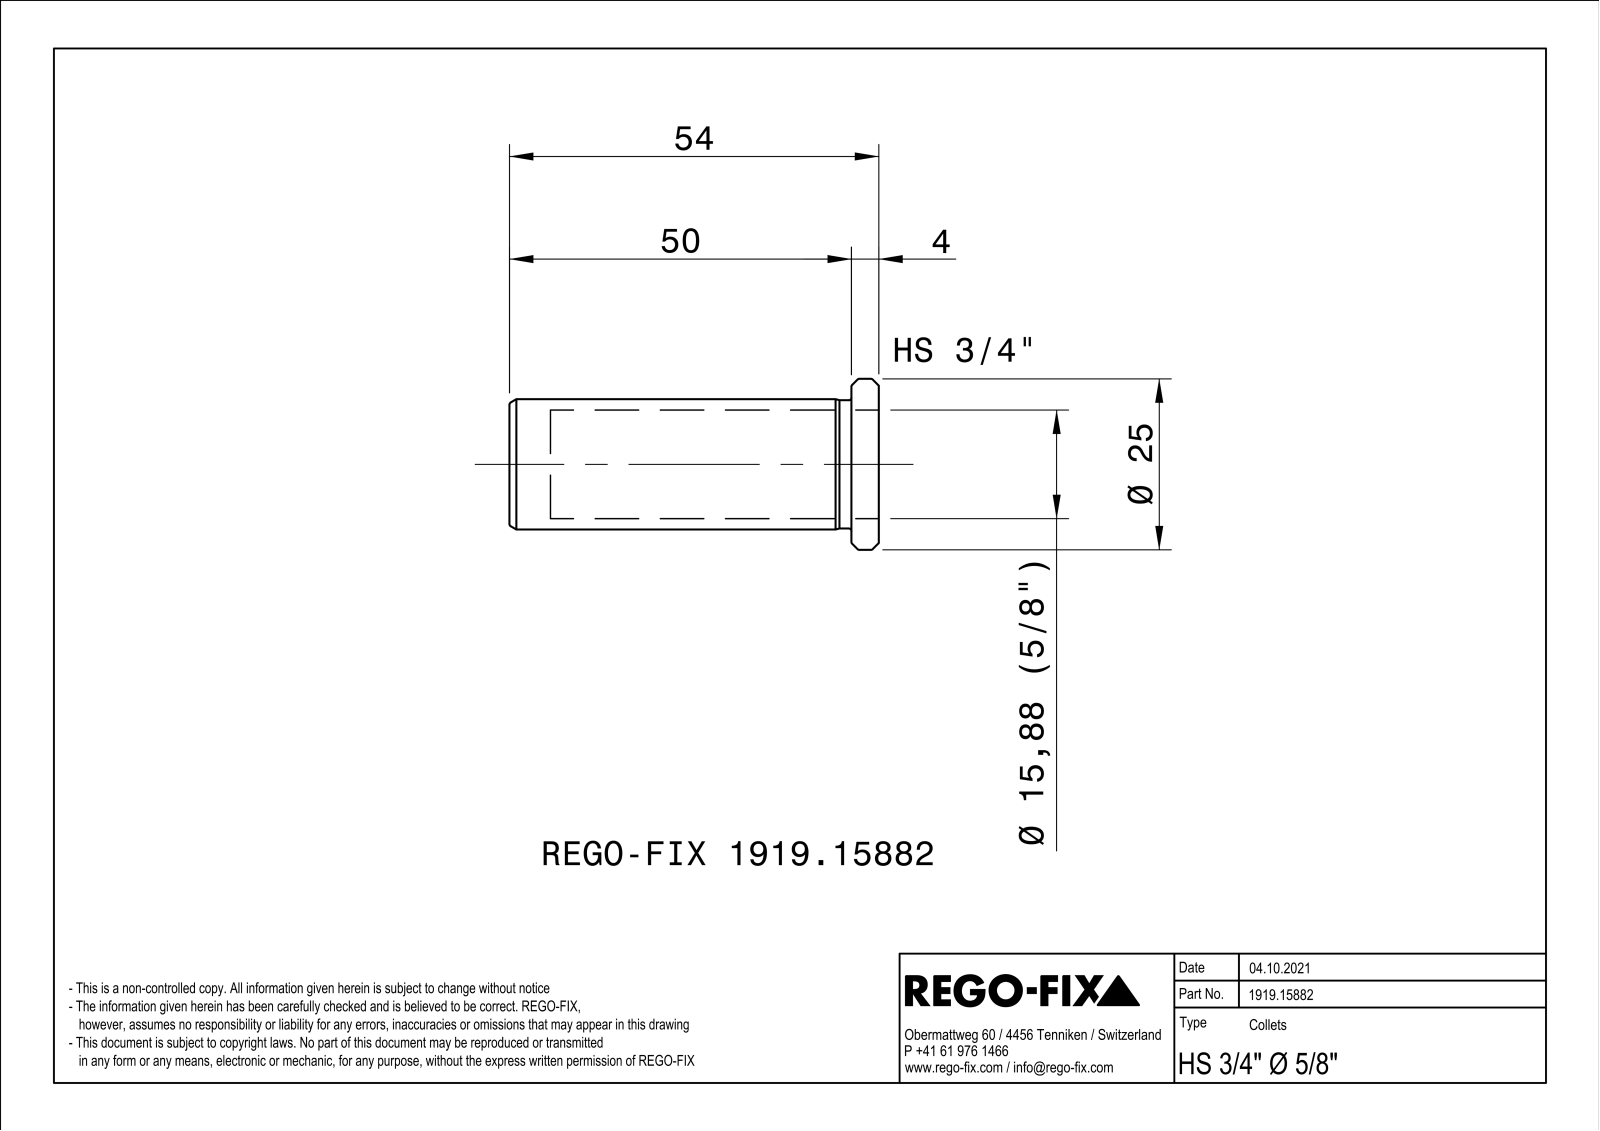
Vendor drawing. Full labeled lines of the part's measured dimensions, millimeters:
Part name (STEP PRODUCT): NOCUT
STEP written by: SIEMENS PLM Software Solid Edge ST10 (AUTOMOTIVE_DESIGN)
Units: millimetres
Bodies: 1 solid, 70 faces (22 planar, 11 cylindrical, 37 other)
Overall size (bounding box): 54 × 24.98 × 24.98
Volume: 4 992 mm³ · Surface area: 6 709 mm²
Round holes (diameter × count): ⌀15.88 ×1, ⌀16.5 ×1
Round bosses / shafts (diameter × count): ⌀25 ×1, ⌀19.05 ×1, ⌀18.75 ×1
Main face-to-face distances: 1, 4, 54, 50
